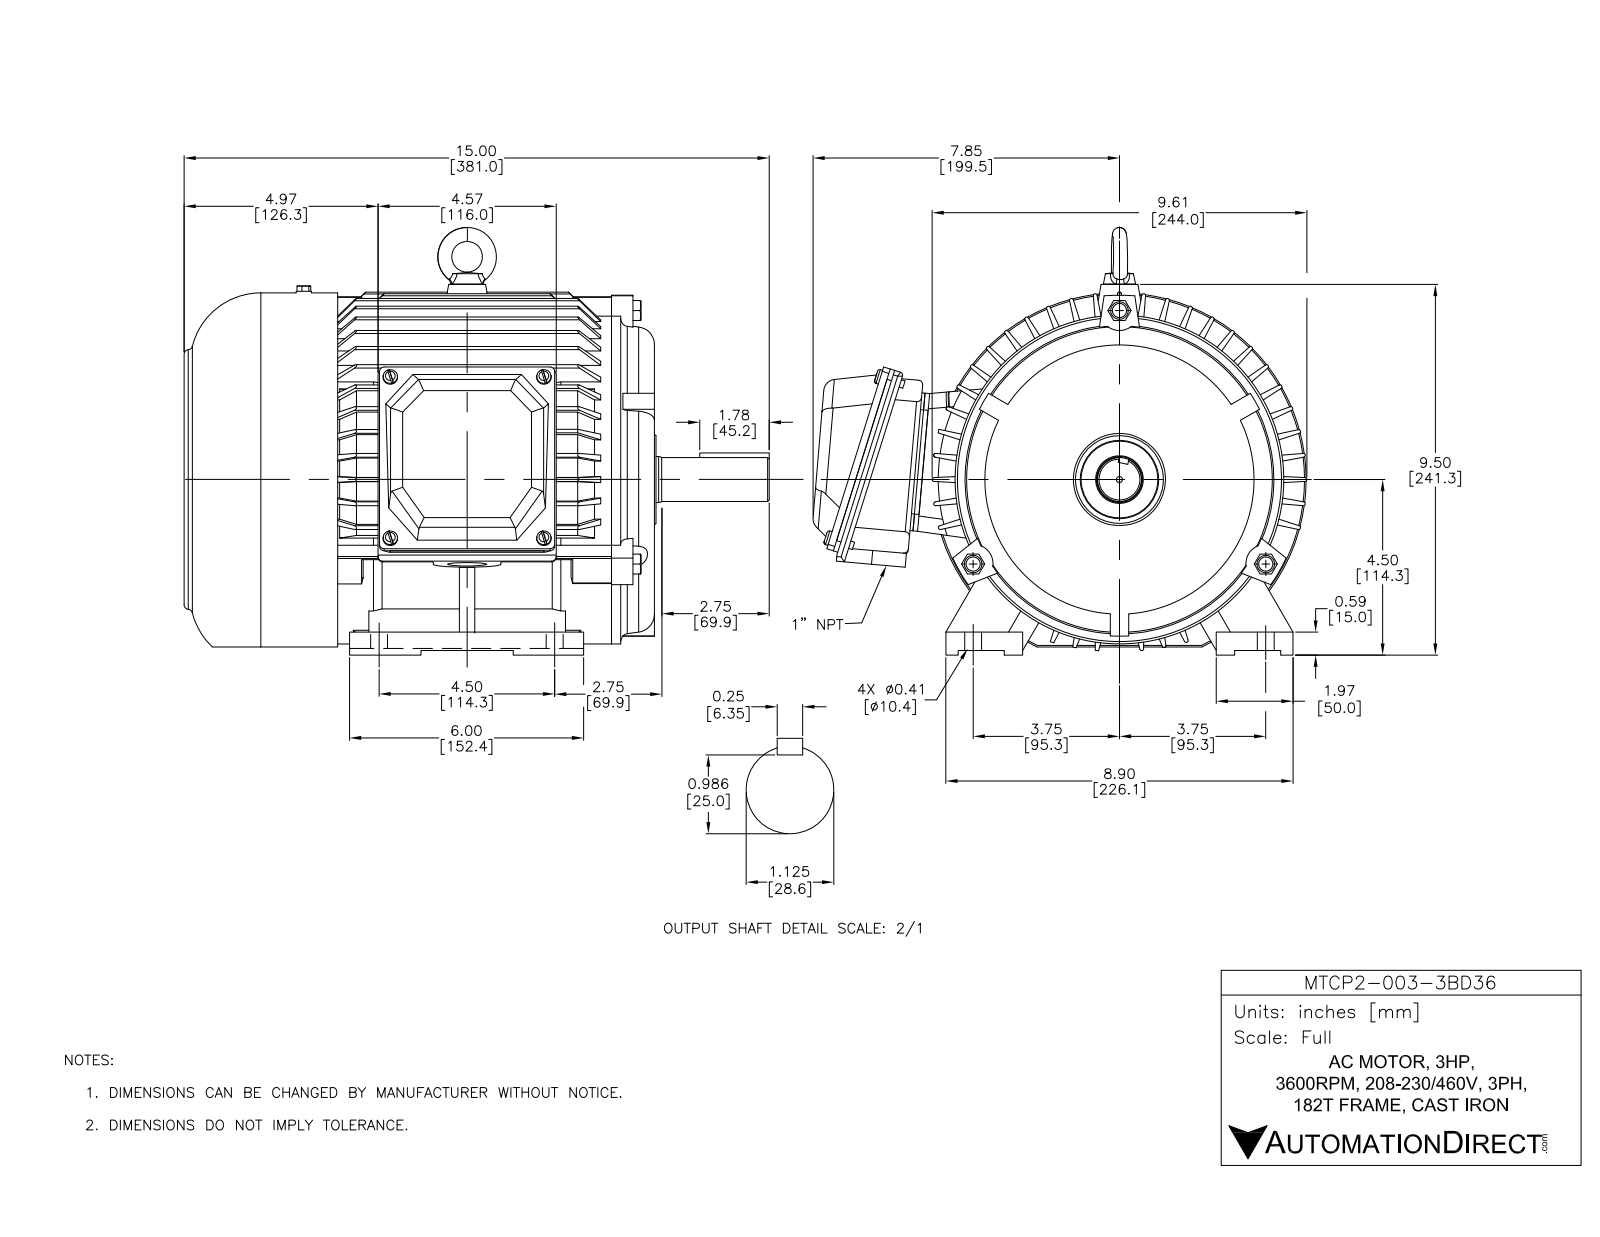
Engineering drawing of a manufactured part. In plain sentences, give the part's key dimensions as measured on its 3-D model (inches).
The part is named "PEWWE-182T". Its 3-D file was written by "SolidWorks 2017 (AUTOMOTIVE_DESIGN)". It is 17 solids with 1658 faces: 766 planar, 568 cylindrical and 324 other. Overall it measures 14.999 by 12.659 by 10.961 inches. Its volume is 504.8 cubic inches and its surface area 1 343 square inches. Round holes: 8 of diameter 0.228, 6 of diameter 0.276, 4 of diameter 0.197, 4 of diameter 0.236, 4 of diameter 0.433, 3 of diameter 0.362, 3 of diameter 0.394, 1 of diameter 0.315, 1 of diameter 1, 1 of diameter 1.181, 1 of diameter 1.969, 1 of diameter 2.047. Round bosses or shafts: 4 of diameter 0.315, 4 of diameter 0.197, 3 of diameter 0.283, 1 of diameter 9.567, 1 of diameter 1.496, 1 of diameter 1.126, 1 of diameter 0.394. Partial cylindrical surfaces (rounded edges, fillets, slot ends): 256 of radius 0.02, 14 of radius 0.118, 9 of radius 0.049, 8 of radius 0.059, 8 of radius 0.157, 8 of radius 0.276, 8 of radius 0.315, 6 of radius 0.091. The main face-to-face distances are 7.402, 0.039, 1.102, 8.504, 0.236, 0.118, 8.268, 11.959, 10.857, 3.456. The hole center spacings are 3.937, 2.677, 3.786, 4.331, 5.853, 2.678, 4.33, 4.331.
